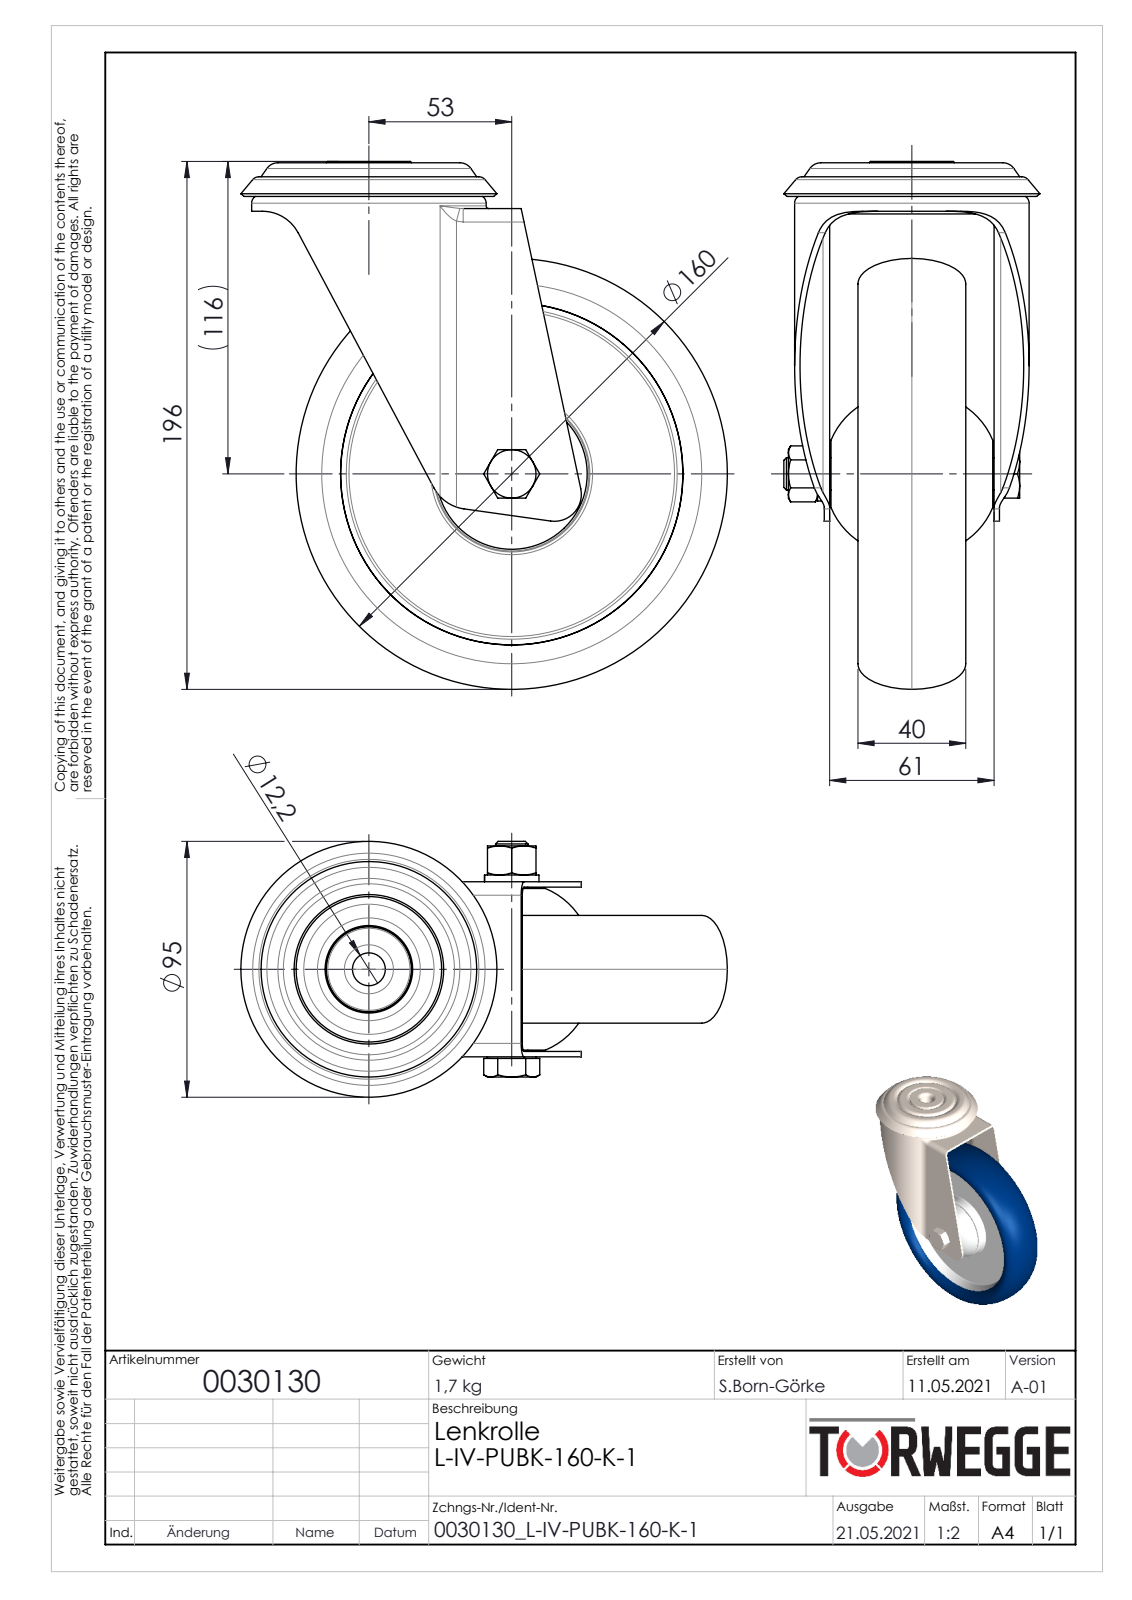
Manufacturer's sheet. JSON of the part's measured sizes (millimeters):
{"part_name": "0030130", "step_written_by": "SolidWorks 2020 (AUTOMOTIVE_DESIGN)", "units": "millimeters", "bodies": {"solids": 8, "faces": 245, "planar": 63, "cylindrical": 54, "other": 128}, "overall_size": [196, 180.5, 95], "volume_mm3": 567553, "surface_area_mm2": 187969, "round_holes": [[12.2, 2], [10.2, 1], [12, 1], [12.3, 1], [45, 1], [47, 1], [83, 1]], "round_bosses_or_shafts": [[87, 1], [41, 1], [31.5, 1], [20.2, 1], [20, 1], [18, 1]], "partial_cylinders_radius": [[10, 3], [3, 2], [5, 2], [12, 2], [15, 2]], "face_to_face_distances": [9.5, 2, 27.75, 37.25, 35.25, 63, 25.75, 65, 61, 1.5]}
